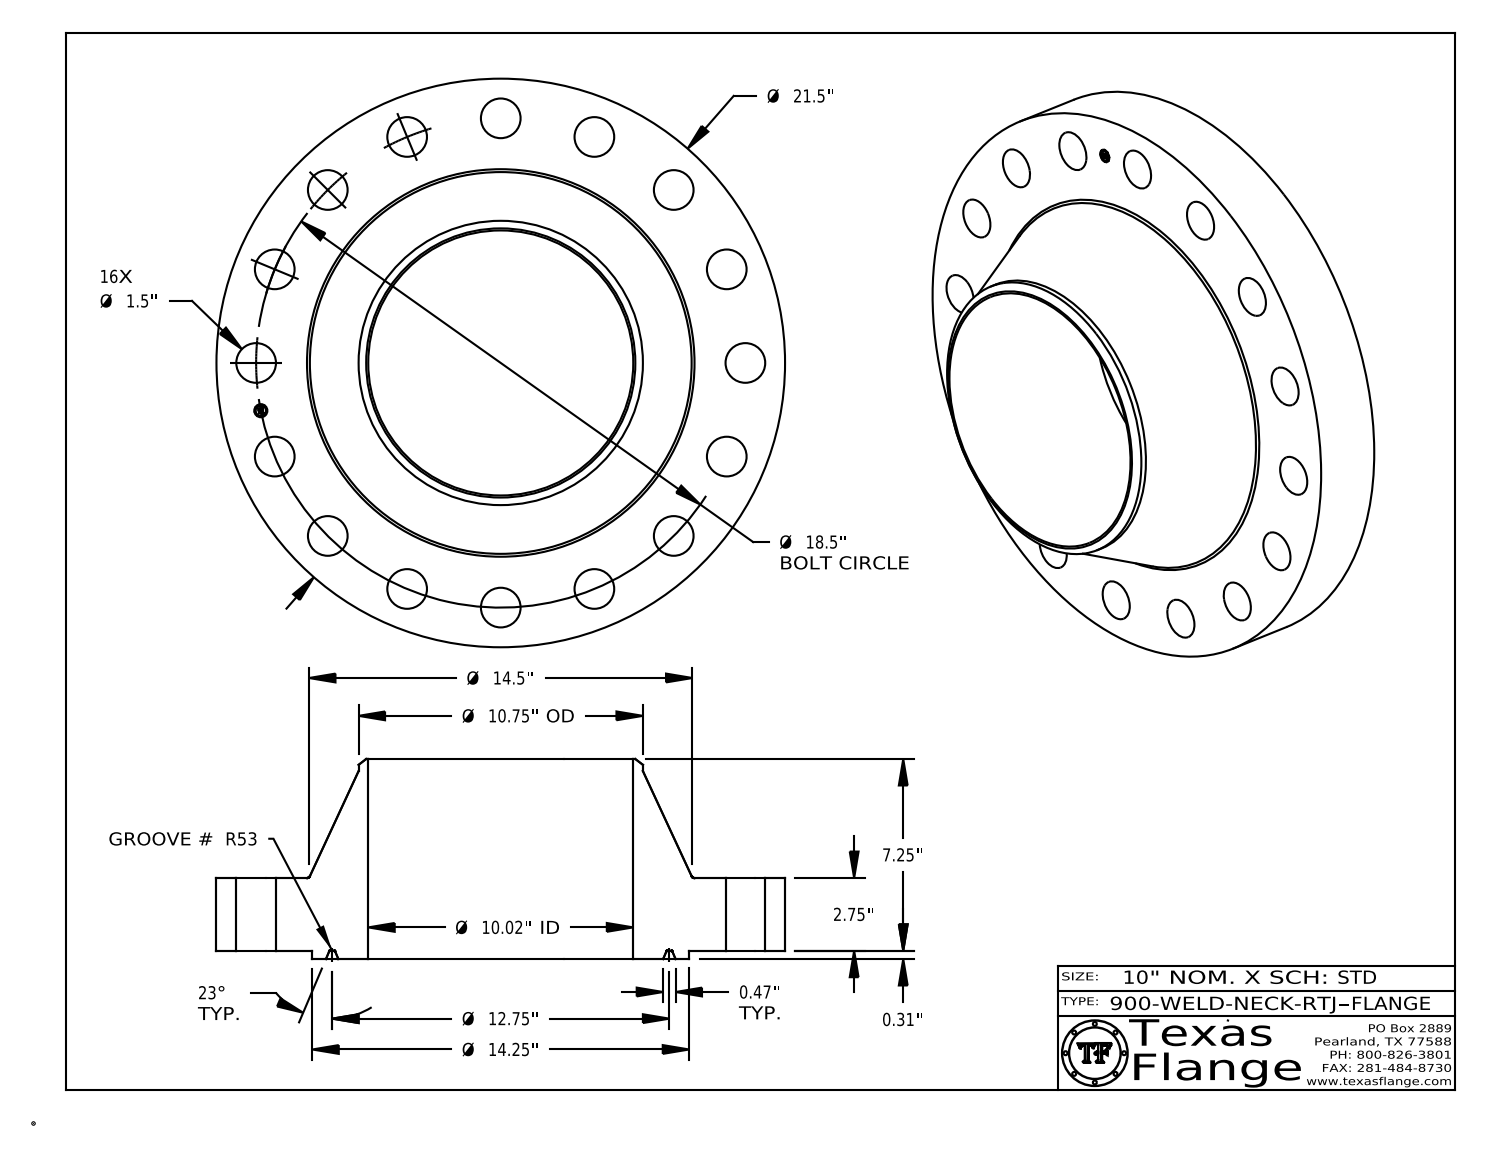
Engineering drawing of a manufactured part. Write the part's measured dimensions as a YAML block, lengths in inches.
part_name: "900-WELD-NECK-RTJ"
step_written_by: "CATIA V5 STEP AP214 (AUTOMOTIVE_DESIGN)"
units: inches
bodies: {solids: 1, faces: 445, planar: 371, cylindrical: 60, other: 14}
overall_size: [21.5, 21.5, 7.563]
volume: 920.3
surface_area: 1285
round_holes:
  - {diameter: 1.5, count: 16}
  - {diameter: 0.495, count: 1}
  - {diameter: 10.02, count: 1}
round_bosses_or_shafts:
  - {diameter: 0.03, count: 8}
  - {diameter: 21.5, count: 1}
  - {diameter: 14.25, count: 1}
  - {diameter: 10.75, count: 1}
  - {diameter: 0.39, count: 1}
face_to_face_distances: [2.75, 0.313, 3.063, 7.563, 7.25, 4.5, 3.048, 2.735, 0.015, 4.515]
hole_center_spacings: [15.382, 7.08, 9.25, 13.081, 3.609, 3.609, 10.278, 10.278]
